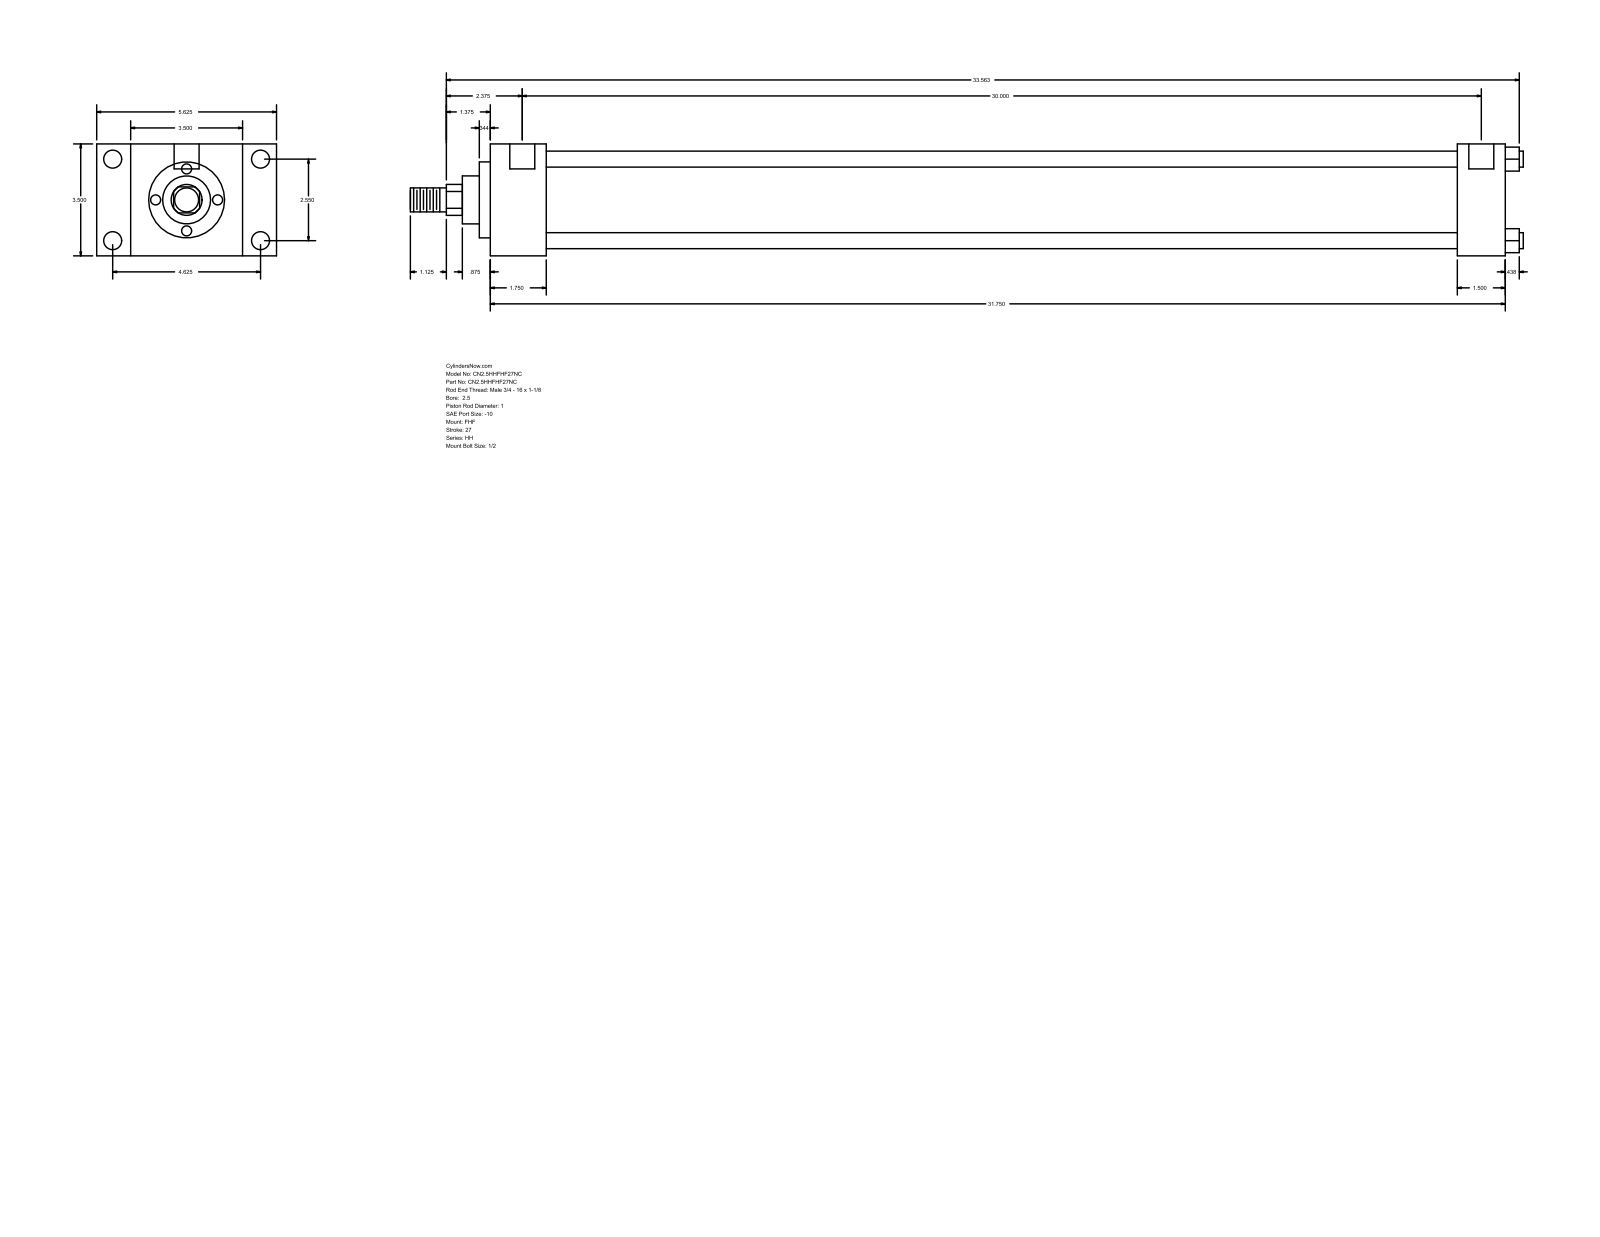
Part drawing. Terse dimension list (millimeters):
name: HH_FHF__0250_1
written by: GSSL Pune (CONFIG_CONTROL_DESIGN)
unit: mm
bodies: 0 solids, 90 faces (61 planar, 29 cylindrical, 0 other)
size: 884.24 × 142.88 × 88.9
holes: 4× ⌀5.56, 4× ⌀14.3, 2× ⌀19.84
bosses: 4× ⌀12.7, 1× ⌀73.03, 1× ⌀60.33, 1× ⌀38.1, 1× ⌀25.4, 1× ⌀19.05
rounds: 1× R12.29
face distances: 88.9, 44.46, 26.99, 115.89, 806.46, 762, 142.88, 768.35, 723.89, 38.11
hole spacings: 64.76, 117.48, 134.15, 765.17, 1.58, 1.59, 762, 763.58
